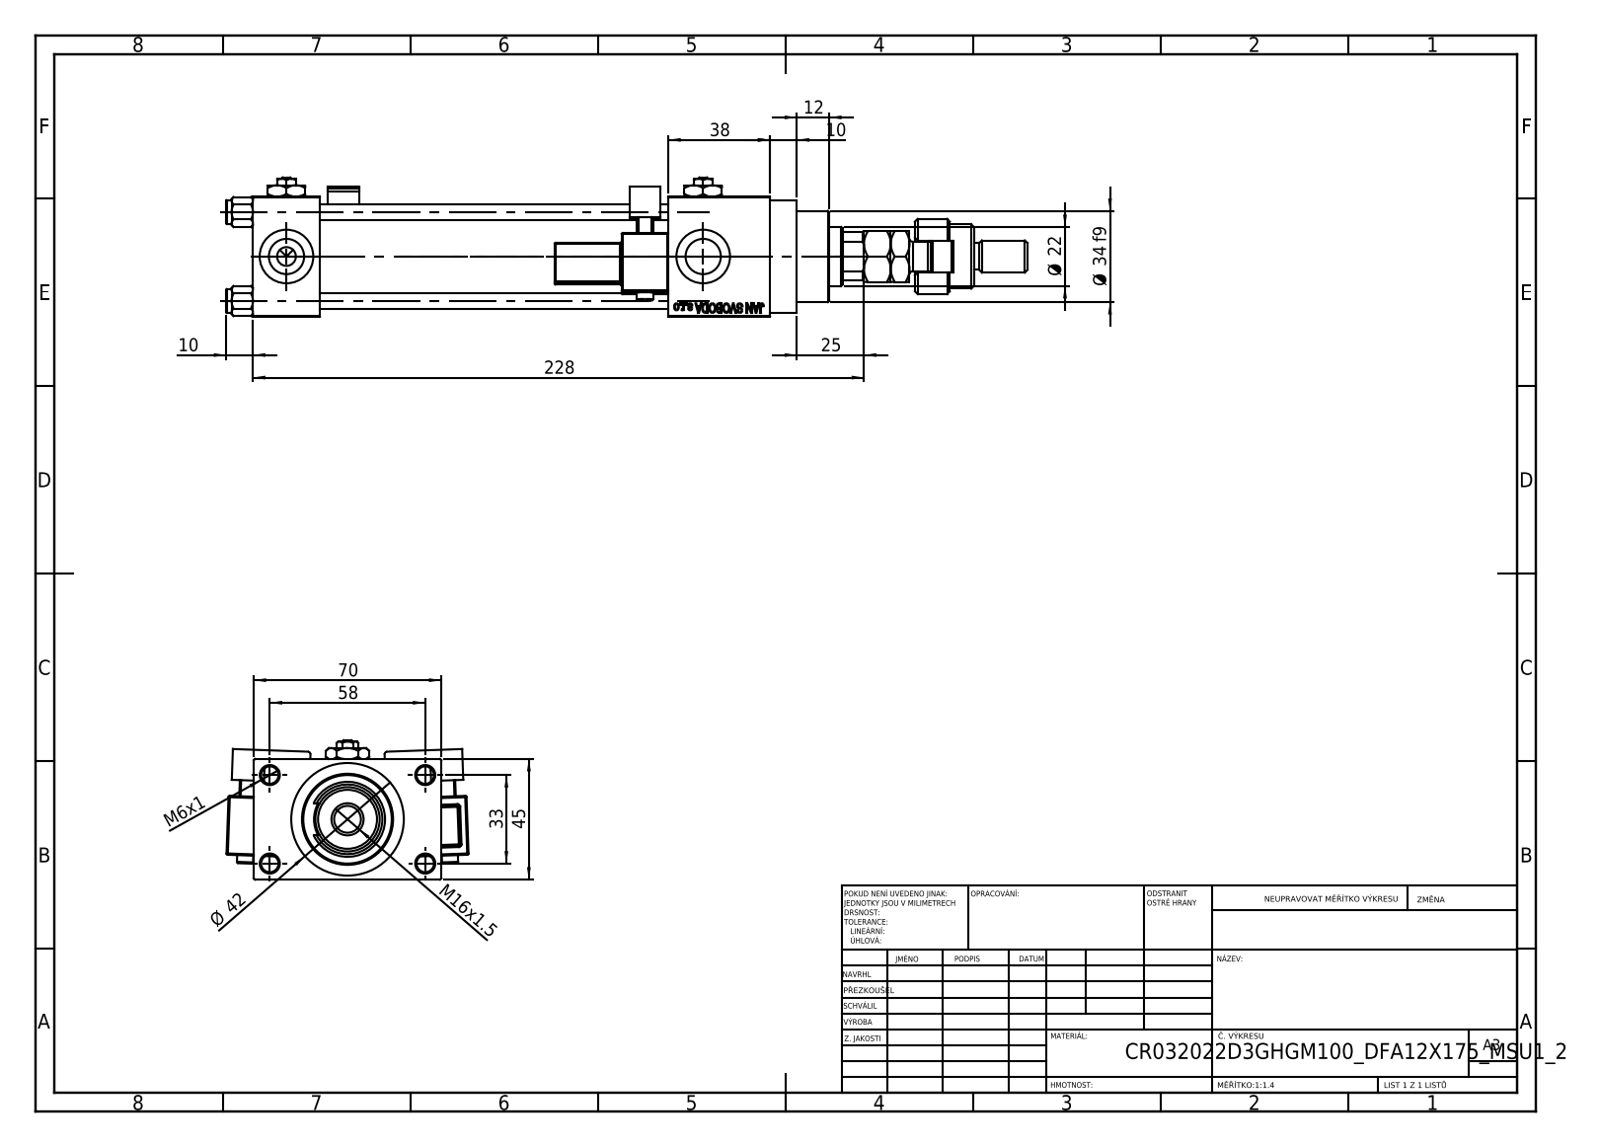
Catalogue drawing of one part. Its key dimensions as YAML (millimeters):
part_name: "V215CR_MSU; V215CR_D_TYCINKA; NUT_M5_D; V215CR_D_Body (+5 more)"
step_written_by: "SolidWorks 2019 (CONFIG_CONTROL_DESIGN)"
units: millimeters
bodies: {solids: 17, faces: 1444, planar: 632, cylindrical: 172, other: 640}
overall_size: [299, 90.31, 52]
volume: 366130
surface_area: 129988
round_holes:
  - {diameter: 6, count: 4}
  - {diameter: 6.5, count: 4}
  - {diameter: 13.16, count: 4}
  - {diameter: 20, count: 4}
  - {diameter: 7, count: 3}
  - {diameter: 10.5, count: 1}
  - {diameter: 22, count: 1}
  - {diameter: 24, count: 1}
  - {diameter: 25, count: 1}
  - {diameter: 32, count: 1}
  - {diameter: 33, count: 1}
round_bosses_or_shafts:
  - {diameter: 9, count: 4}
  - {diameter: 6, count: 2}
  - {diameter: 42, count: 1}
  - {diameter: 38, count: 1}
  - {diameter: 34, count: 1}
  - {diameter: 28, count: 1}
  - {diameter: 18, count: 1}
  - {diameter: 12, count: 1}
partial_cylinders:
  - {radius: 0.5, count: 48}
  - {radius: 1, count: 2}
  - {radius: 2.5, count: 2}
  - {radius: 4, count: 2}
  - {radius: 9.75, count: 1}
  - {radius: 10.5, count: 1}
face_to_face_distances: [45, 25, 130, 12.5, 57.5, 3, 155, 168, 38, 193]
hole_center_spacings: [12.4, 23.48, 33.2, 33.37, 35.35, 45.6, 56.35, 33]
